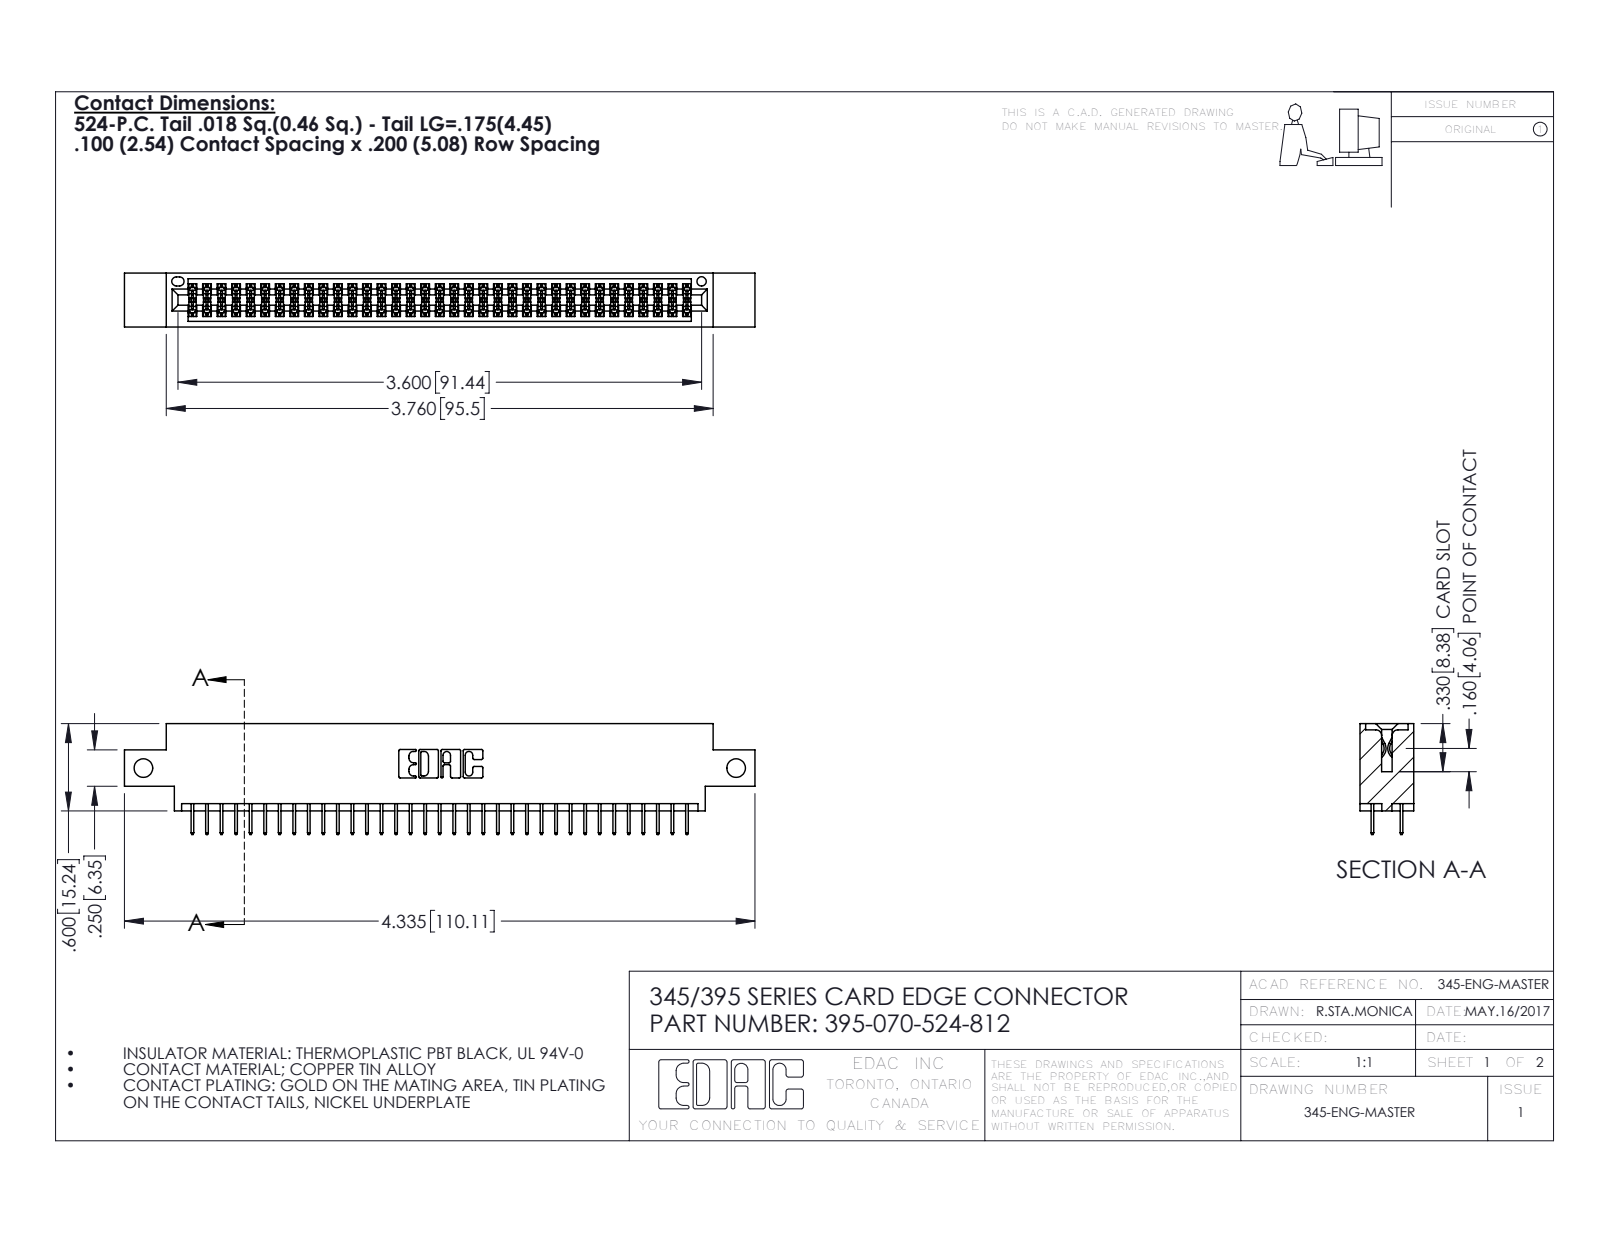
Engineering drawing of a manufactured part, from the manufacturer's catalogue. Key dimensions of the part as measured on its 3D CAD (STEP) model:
Part name (STEP PRODUCT): 345 Part_0.170 Offset - Side Mount; 345-292-001_345-293-124; 395-070-524-812
STEP written by: SolidWorks 2016 (CONFIG_CONTROL_DESIGN)
Units: inches
Bodies: 71 solids, 3910 faces (2814 planar, 1096 cylindrical, 0 other)
Overall size (bounding box): 4.335 × 0.762 × 0.37
Volume: 0.63 in³ · Surface area: 23.02 in²
Round holes (diameter × count): ⌀0.128 ×2, ⌀0.064 ×1
Partial cylindrical surfaces — rounded edges, fillets, slot ends (radius × count): R0.006 ×105, R0.01 ×22, R0.007 ×6, R0.031 ×6, R0.026 ×3, R0.014 ×2, R0.019 ×2, R0.022 ×2
Main face-to-face distances: 0.072, 0.298, 0.37, 0.2, 0.098, 0.272, 0.025, 0.225, 0.175, 0.072
Hole centre spacings: 4.075
